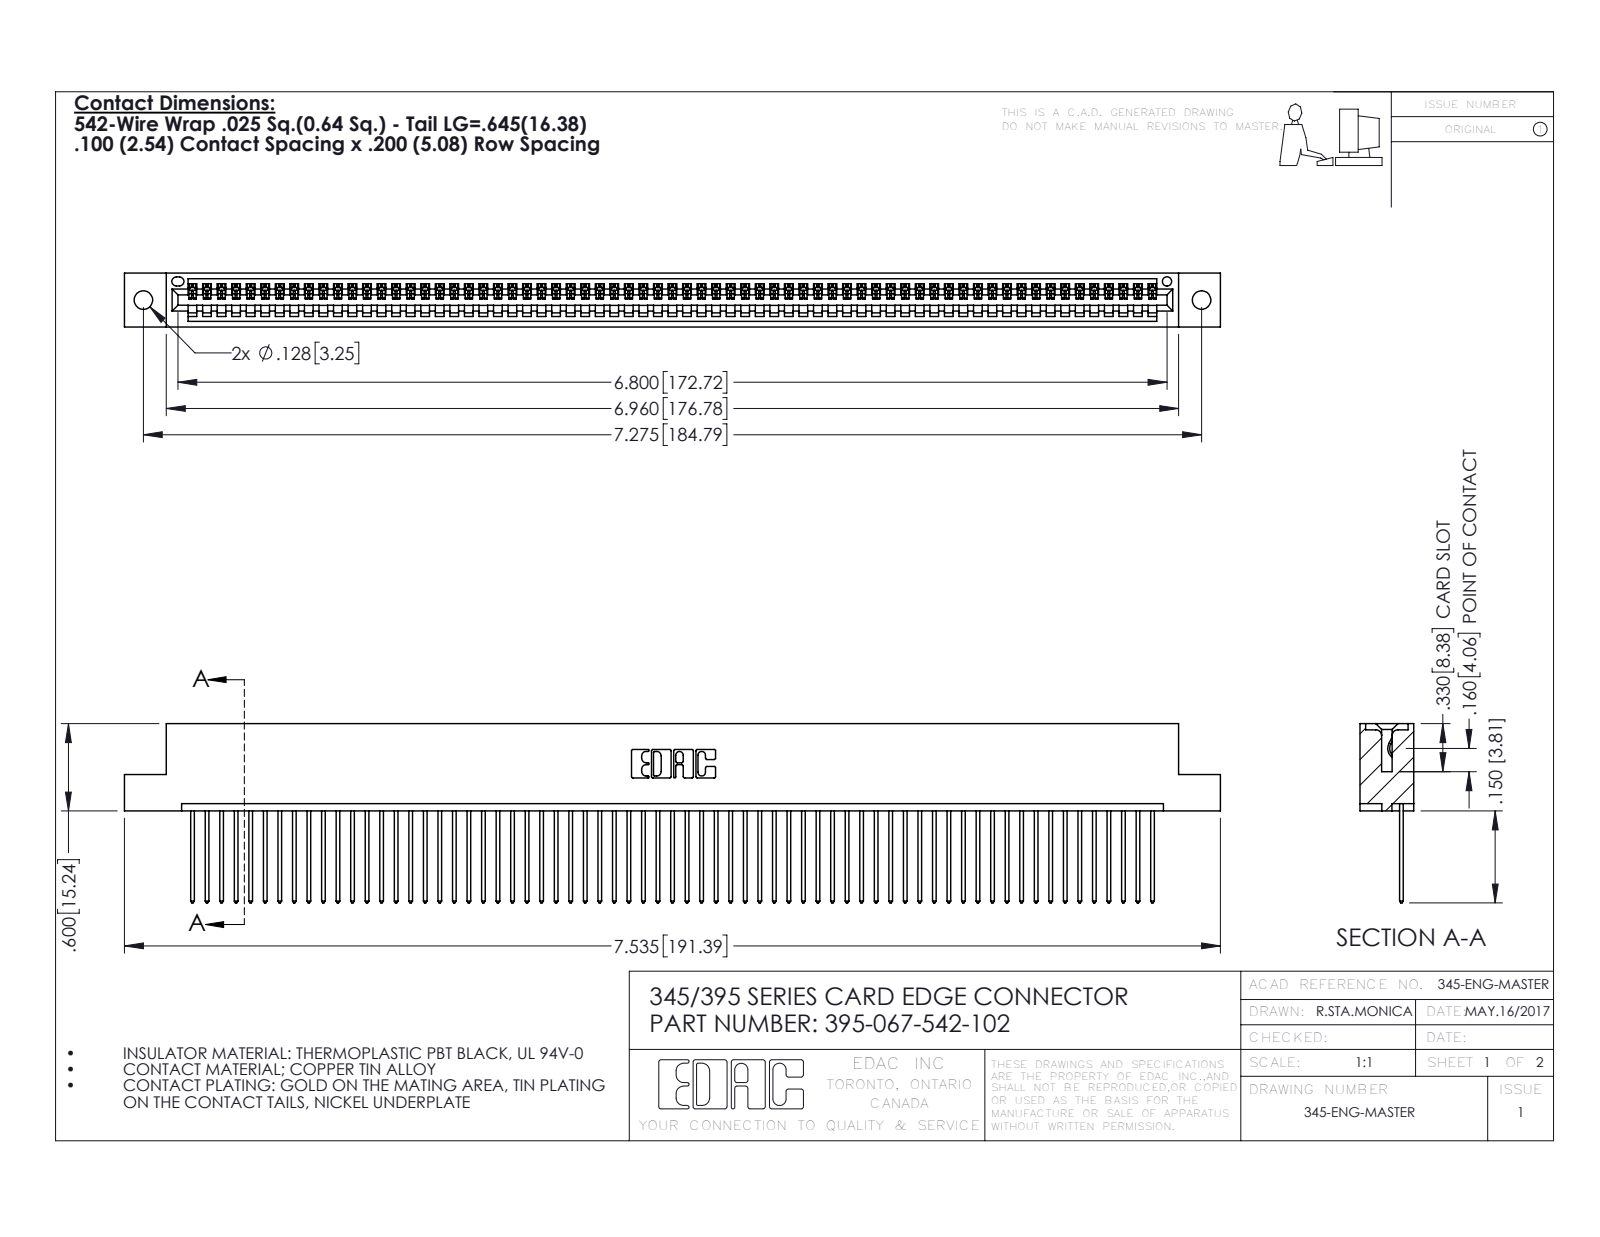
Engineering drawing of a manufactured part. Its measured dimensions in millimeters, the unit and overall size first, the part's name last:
Units: millimetres
Overall size (bounding box): 191.4 × 31.3 × 9.4
Round holes (diameter × count): ⌀3.3 ×2, ⌀1.6 ×1
Partial cylindrical surfaces — rounded edges, fillets, slot ends (radius × count): R0.2 ×134, R0.3 ×134, R0.3 ×22, R0.2 ×6, R0.8 ×6, R0.7 ×3, R0.8 ×2, R1 ×2
Main face-to-face distances: 1.8, 7.6, 2.5, 6.9, 0.6, 9.4, 5.1, 5.7, 3.8, 1.8
Hole centre spacings: 6.9, 178.8, 184.8
Volume: 18 500 mm³ · Surface area: 25 590 mm²
Bodies: 68 solids, 4012 faces (2760 planar, 1252 cylindrical, 0 other)
Part name (STEP PRODUCT): 345 Part_Flush Mounting Lugs - 0.128 Dia; 395-067-542-102; 345-292-001_345-293-142
STEP written by: SolidWorks 2016 (CONFIG_CONTROL_DESIGN)
